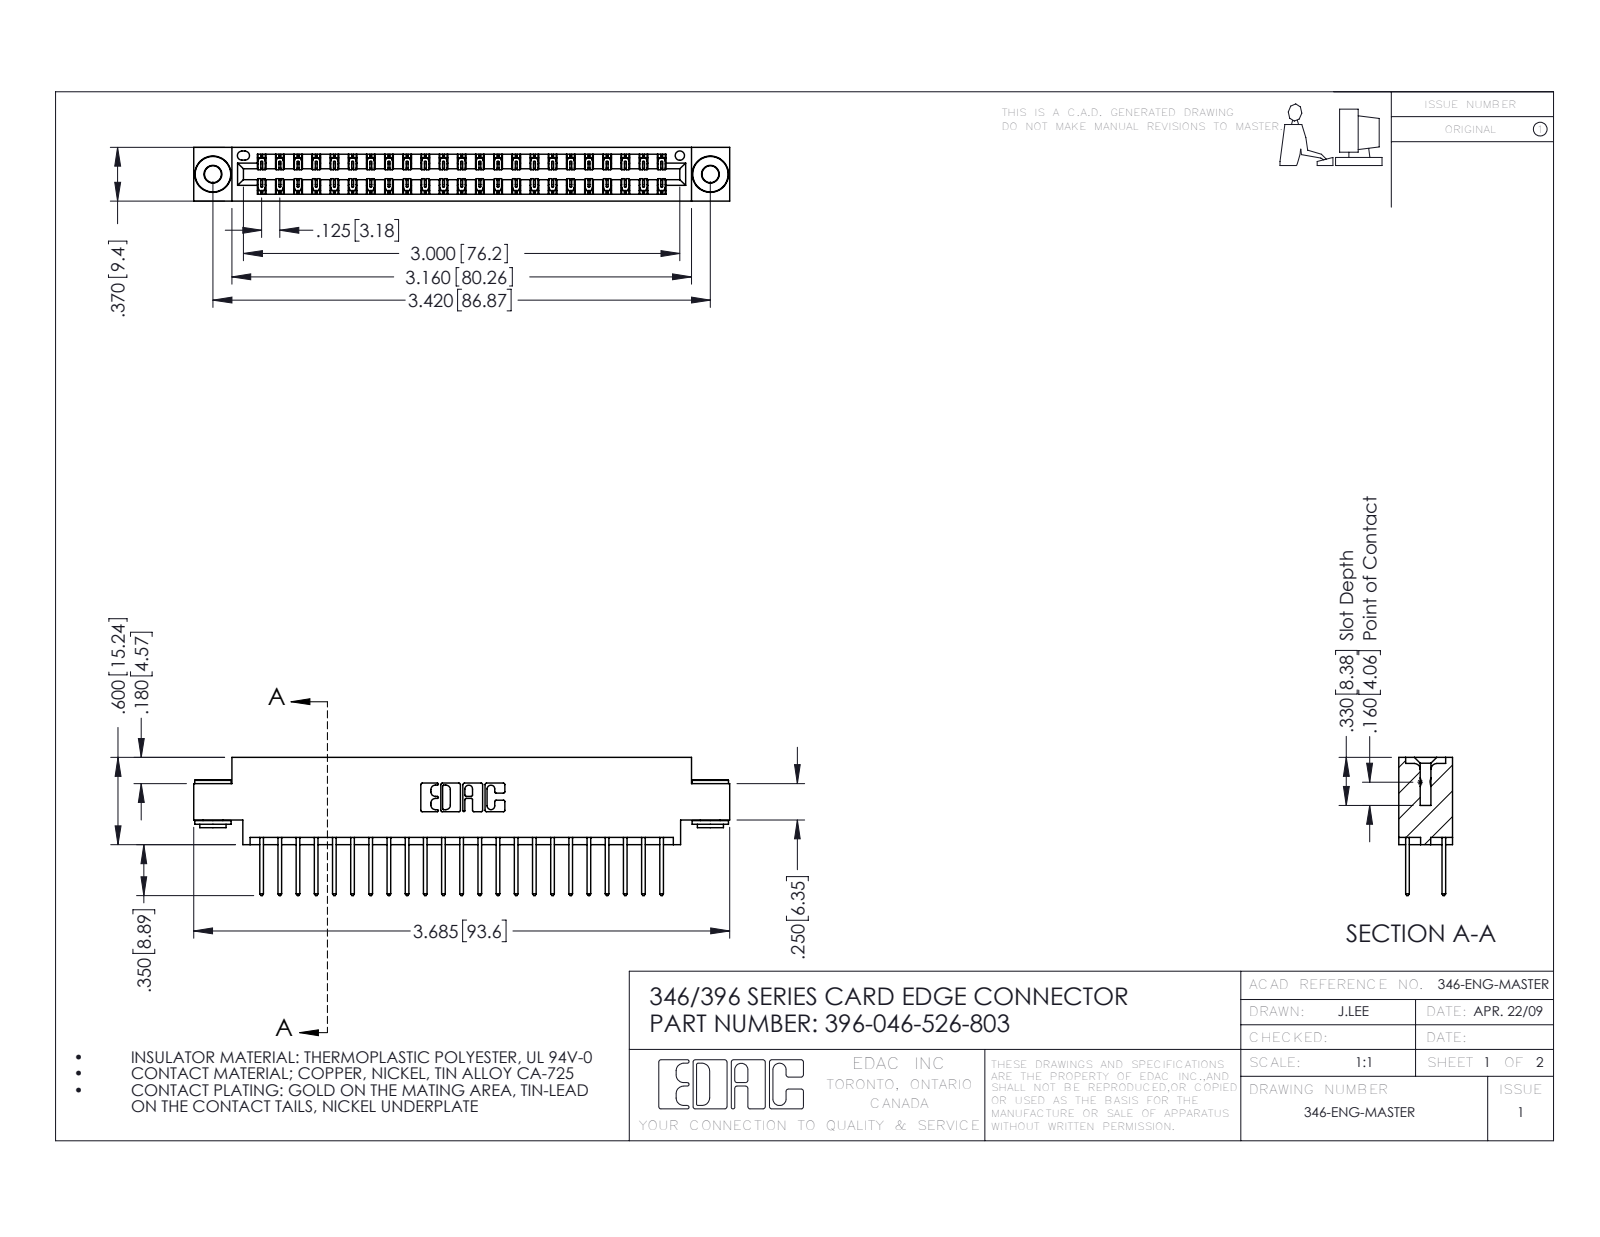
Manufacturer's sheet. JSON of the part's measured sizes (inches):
{"part_name": "346 Part_0.170 Offset - 0.156 Dia-TH; 345-292-001_345-293-126; 345-250-002_345-250-002-102; 396-046-526-803", "step_written_by": "SolidWorks 2016 (CONFIG_CONTROL_DESIGN)", "units": "inches", "bodies": {"solids": 49, "faces": 2556, "planar": 1700, "cylindrical": 848, "other": 8}, "overall_size": [3.685, 0.95, 0.37], "volume_in3": 0.544, "surface_area_in2": 19.68, "round_holes": [[0.116, 2], [0.156, 2], [0.064, 1]], "round_bosses_or_shafts": [[0.25, 2], [0.18, 2], [0.136, 2]], "partial_cylinders_radius": [[0.006, 69], [0.01, 46], [0.01, 22], [0.007, 6], [0.031, 6], [0.026, 3], [0.014, 2], [0.022, 2]], "face_to_face_distances": [0.048, 0.322, 0.25, 0.37, 0.025, 0.072, 0.298, 0.275, 0.148, 0.222], "hole_center_spacings": [0.246, 3.212, 3.42]}
